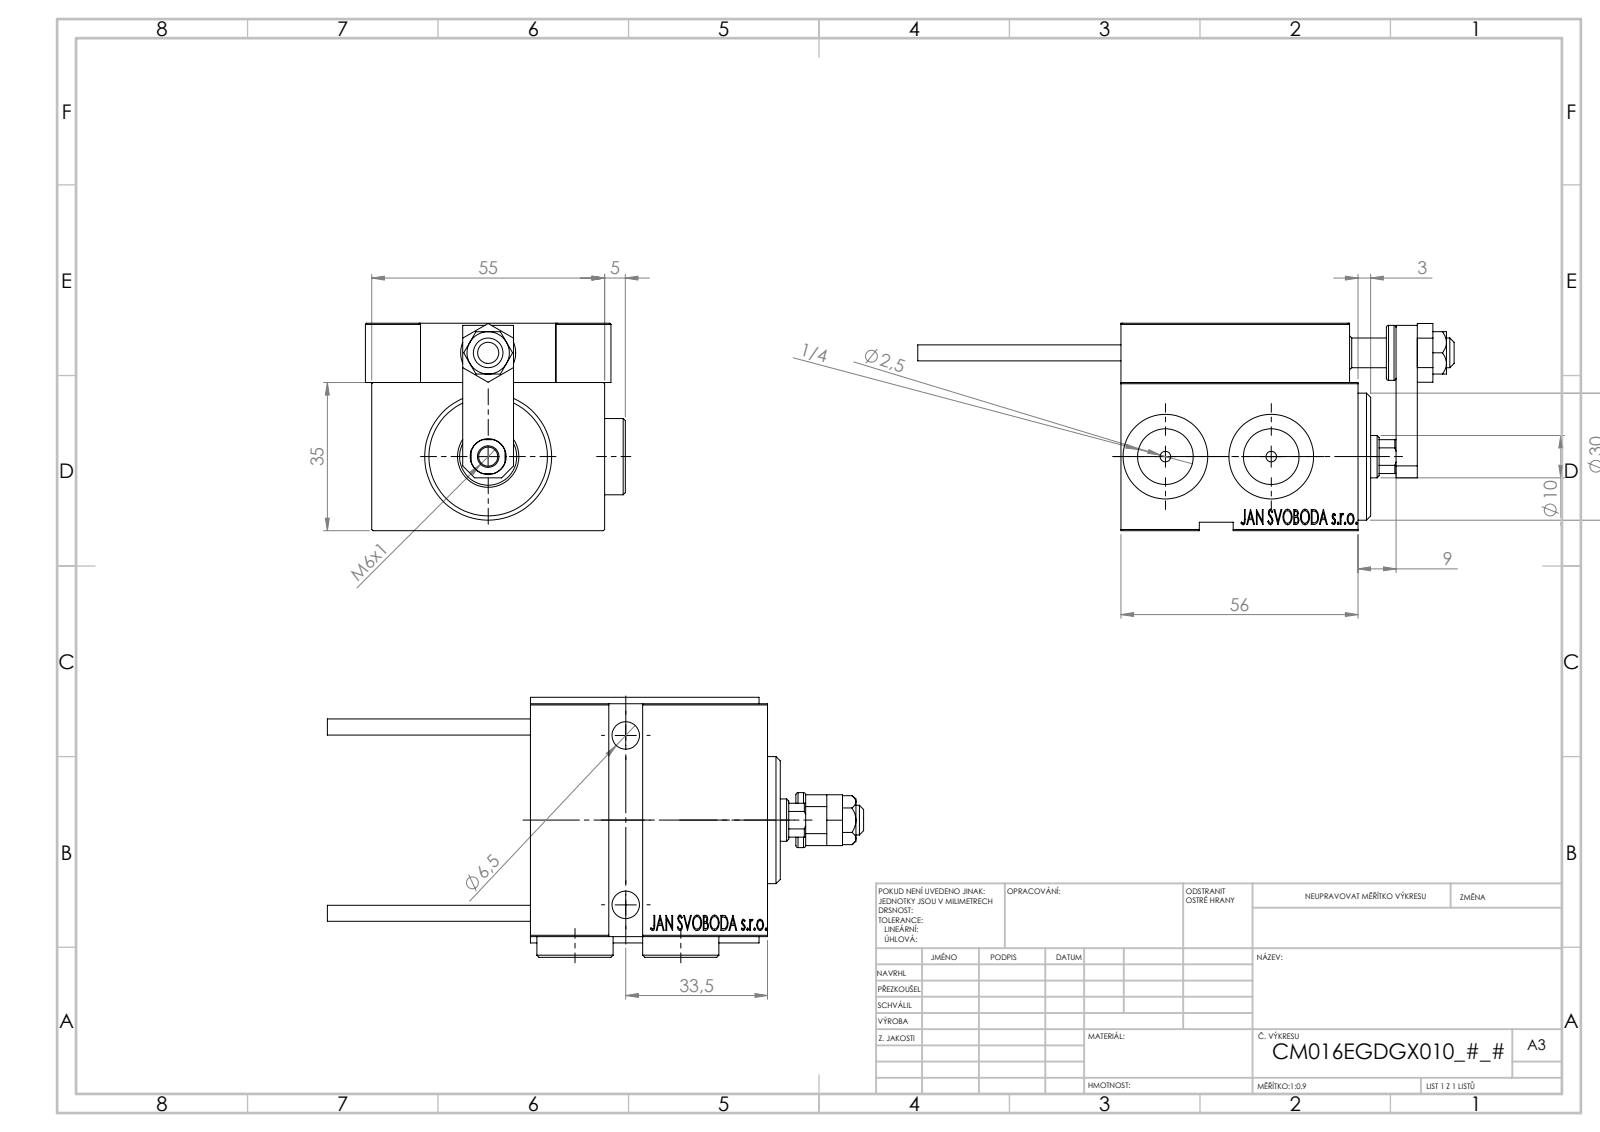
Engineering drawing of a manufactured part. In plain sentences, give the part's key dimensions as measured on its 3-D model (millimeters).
The part is named "V450CM_E_VCP; V450CM_E_Body; SWITCH DIM B,W; MAGNET (+7 more)". Its 3-D file was written by "SolidWorks 2019 (CONFIG_CONTROL_DESIGN)". It is 26 solids with 1340 faces: 603 planar, 192 cylindrical and 545 other. Overall it measures 126.7 by 61.4 by 49 millimeters. Its volume is 142 543 cubic millimeters and its surface area 50 075 square millimeters. Round holes: 5 of diameter 8, 4 of diameter 3.2, 4 of diameter 4, 2 of diameter 2.5, 2 of diameter 5, 2 of diameter 6.5, 2 of diameter 10.5, 2 of diameter 13.16, 2 of diameter 20, 1 of diameter 4.5, 1 of diameter 7, 1 of diameter 8.5. Round bosses or shafts: 3 of diameter 18, 2 of diameter 5, 2 of diameter 3.8, 1 of diameter 30, 1 of diameter 13, 1 of diameter 11. Partial cylindrical surfaces (rounded edges, fillets, slot ends): 26 of radius 0.3, 2 of radius 3, 1 of radius 4.5. The main face-to-face distances are 14, 35, 49, 5, 1.5, 10, 3, 55, 7, 56. The hole center spacings are 20.16, 8.25, 11.37, 20, 23.41, 28.32, 29.59, 29.69.
